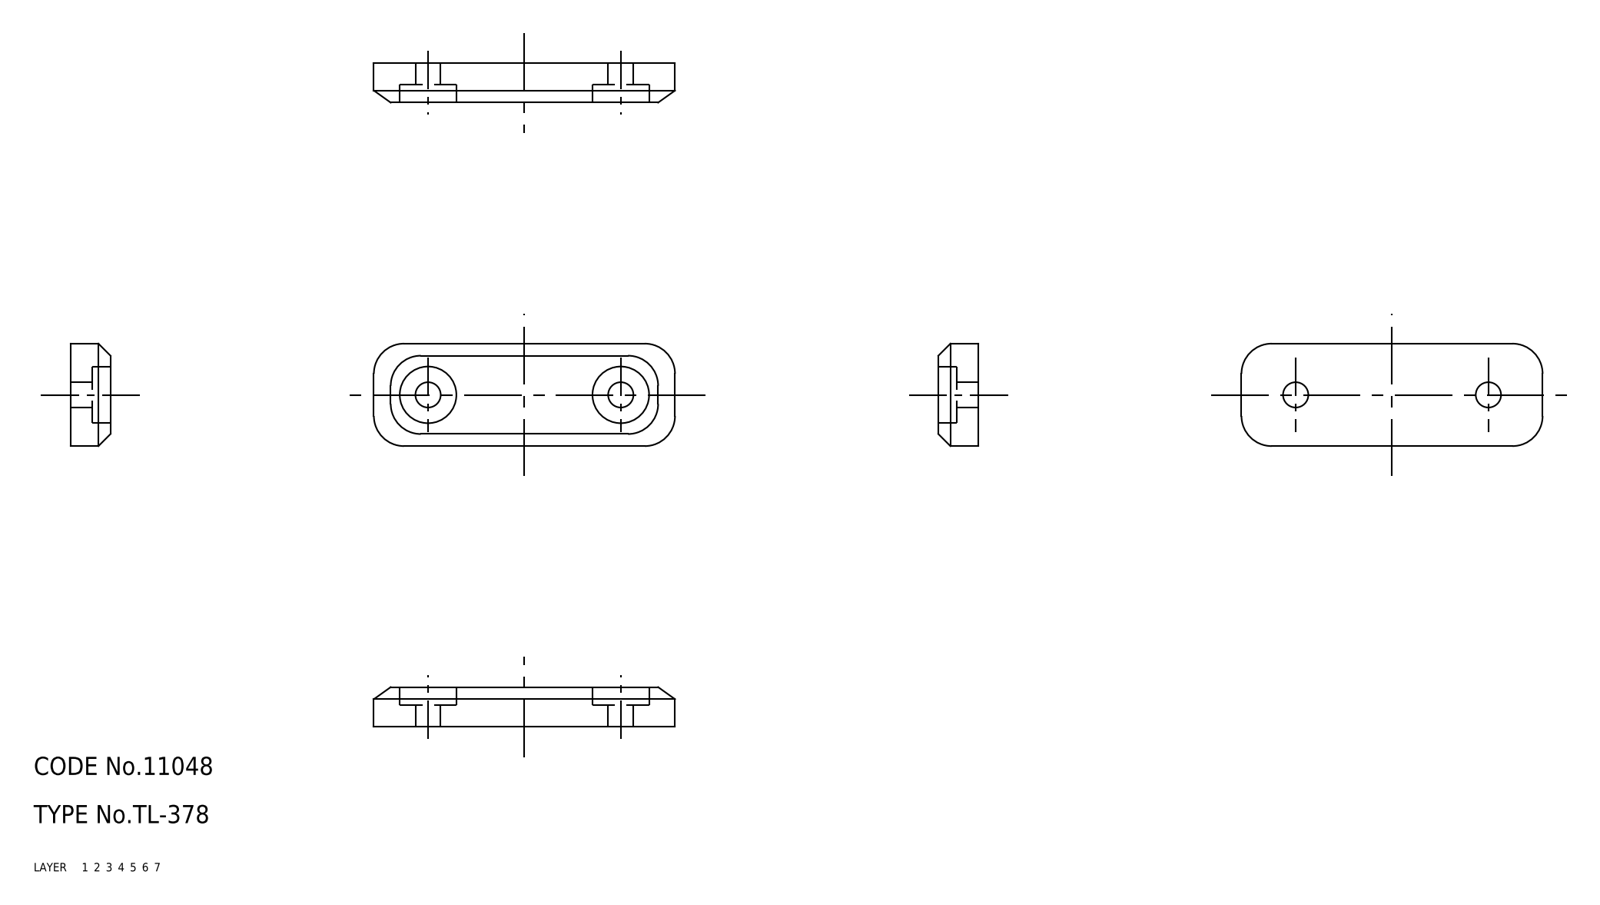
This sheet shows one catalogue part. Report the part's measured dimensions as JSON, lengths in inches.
{"part_name": "67110482", "step_written_by": "CADfix (AUTOMOTIVE_DESIGN)", "units": "inches", "bodies": {"solids": 1, "faces": 28, "planar": 0, "cylindrical": 0, "other": 28}, "overall_size": [1.969, 0.669, 0.26], "volume_in3": 0.287, "surface_area_in2": 3.949}
